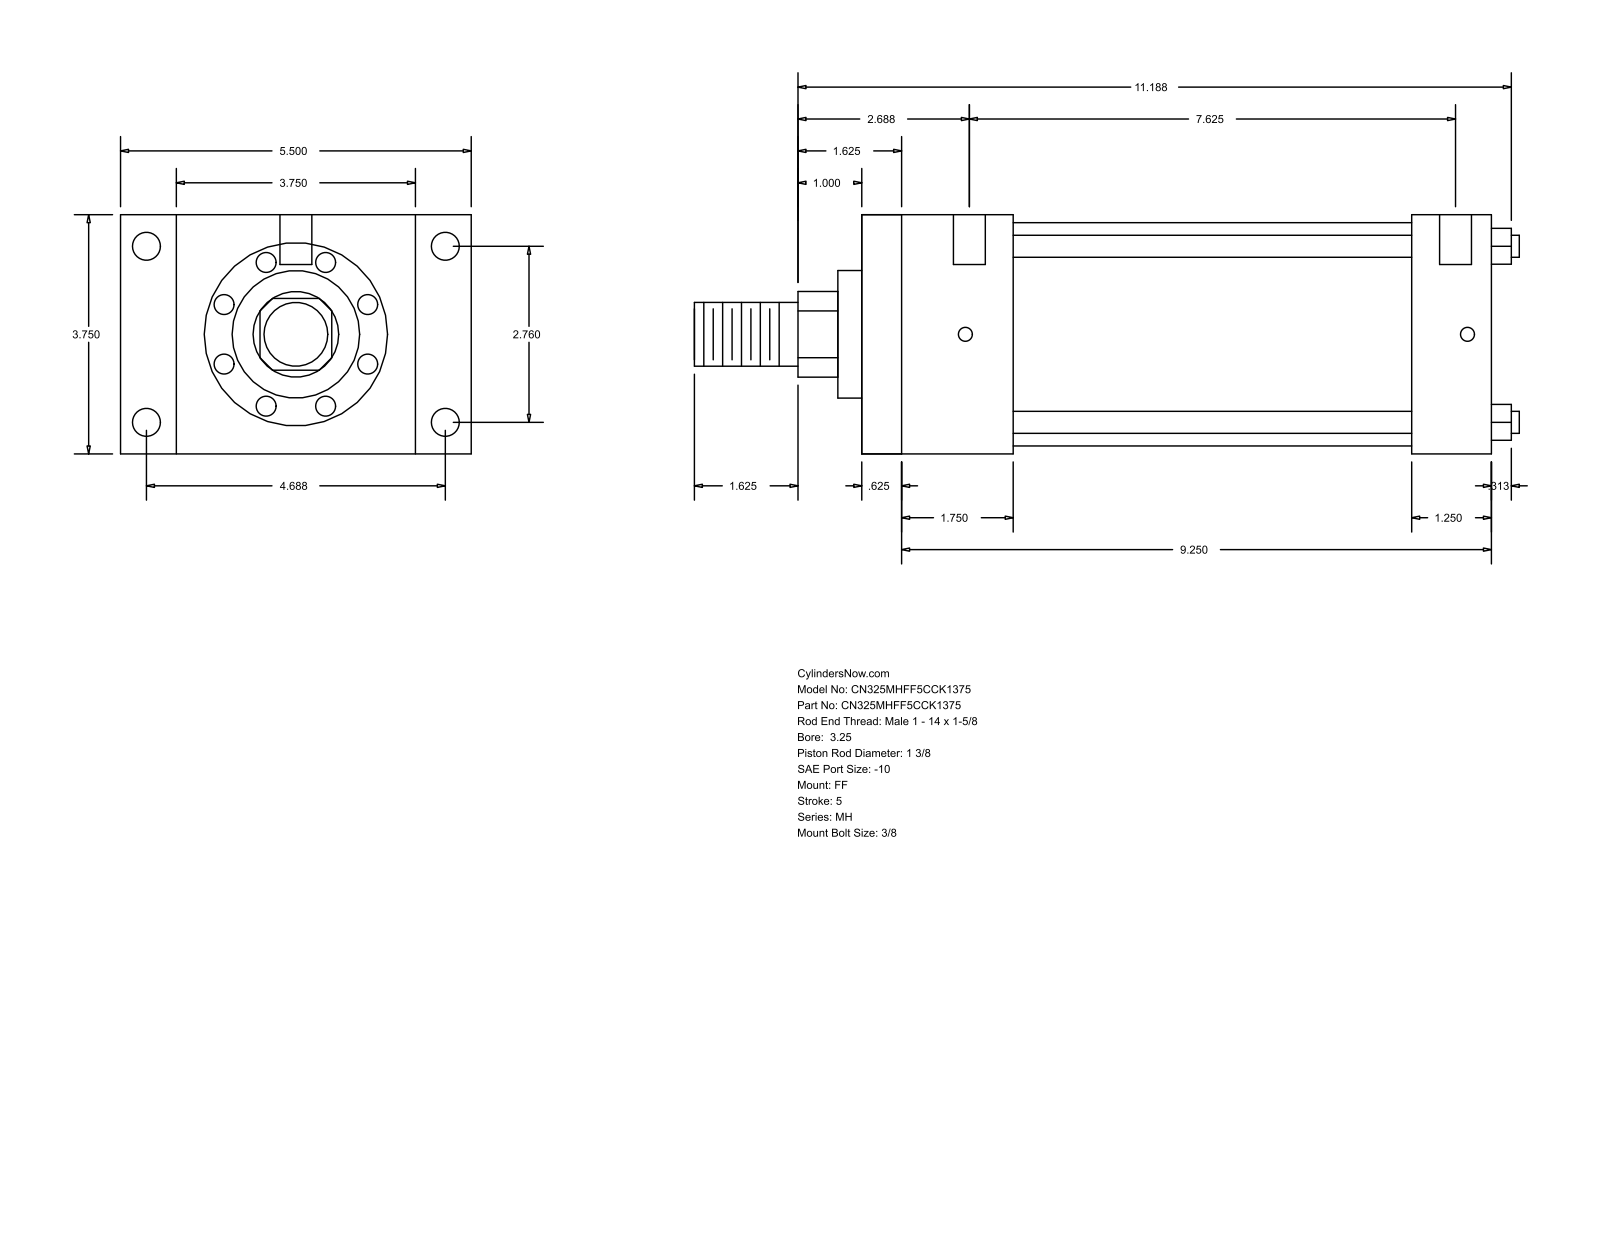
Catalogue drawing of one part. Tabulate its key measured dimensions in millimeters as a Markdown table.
| quantity | value |
| --- | --- |
| part name | MH_FF__0325_1.375 |
| STEP written by | GSSL Pune (CONFIG_CONTROL_DESIGN) |
| units | millimeters |
| bodies | 0 solids, 92 faces (64 planar, 28 cylindrical, 0 other) |
| overall size | 328.61 × 139.7 × 95.25 |
| round holes (diameter × count) | 5.56 × 4, 11.13 × 4, 12.7 × 2 |
| round bosses / shafts (diameter × count) | 8.76 × 4, 88.9 × 1, 50.8 × 1, 34.92 × 1, 25.4 × 1 |
| partial cylindrical surfaces (radius × count) | 17.06 × 1 |
| main face-to-face distances | 95.24, 250.83, 15.87, 234.96, 22.23, 117.47, 219.07, 203.2, 31.76, 60.32 |
| hole center spacings | 70.1, 119.06, 138.16, 200.03, 1.59, 4.76, 193.68, 195.27 |
